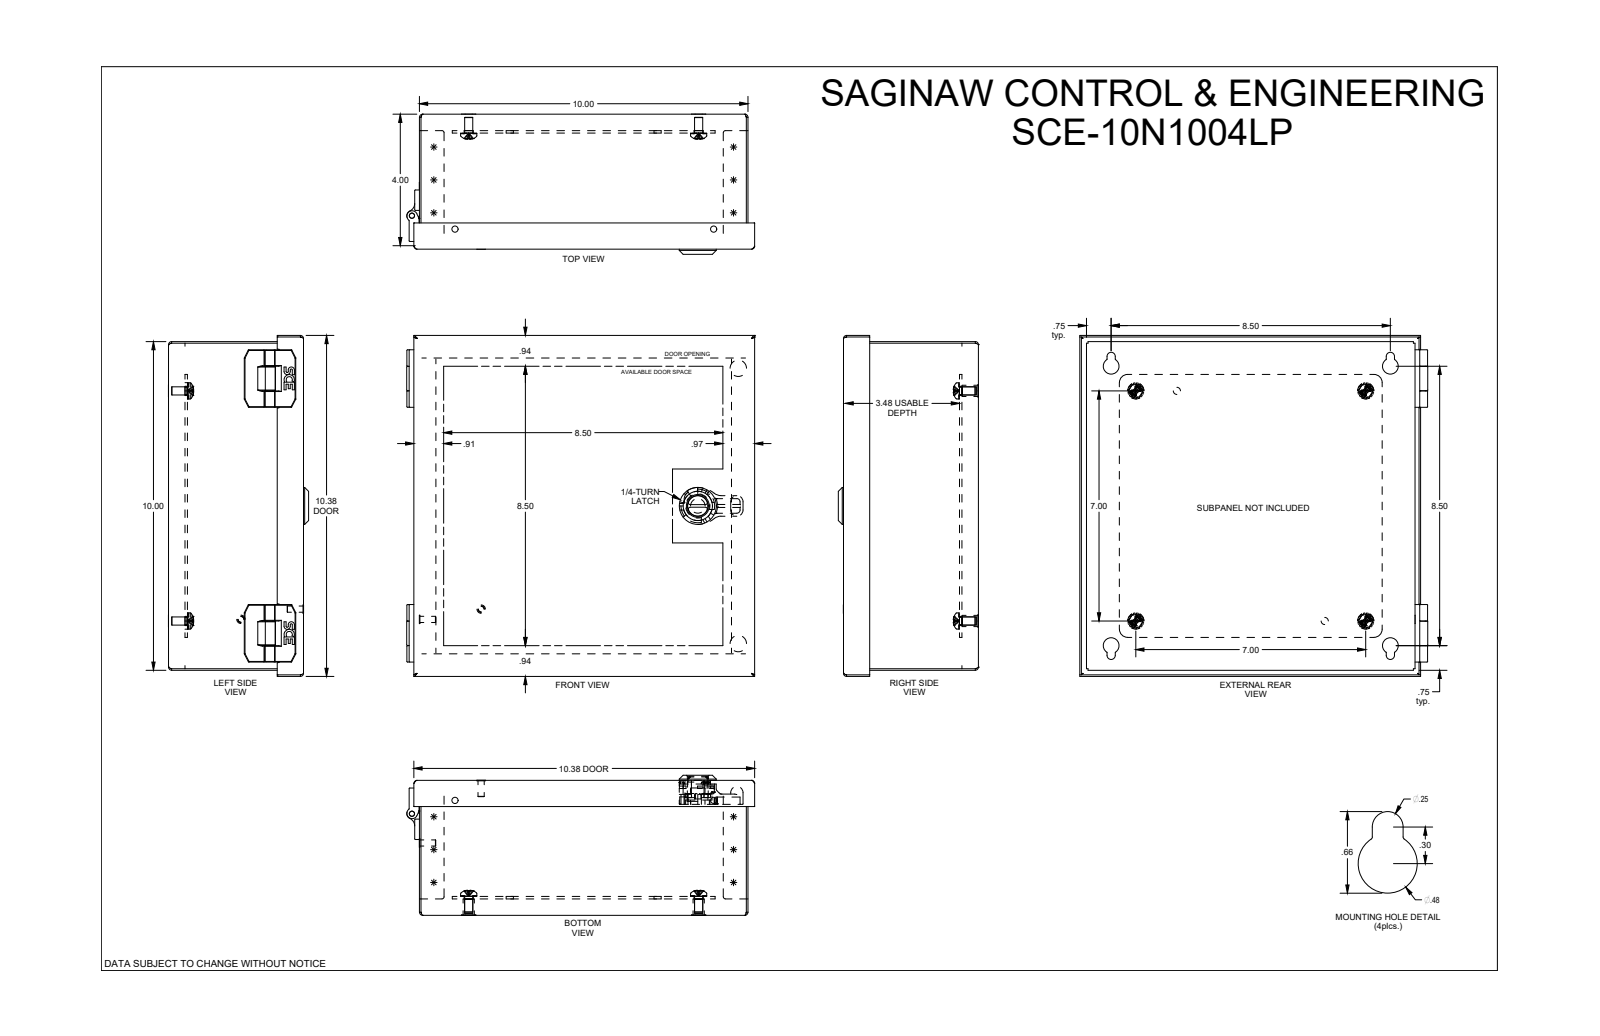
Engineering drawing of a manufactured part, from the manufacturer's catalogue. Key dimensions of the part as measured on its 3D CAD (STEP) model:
Part name (STEP PRODUCT): SCE-10N1004LP
STEP written by: SolidWorks 2019 (AUTOMOTIVE_DESIGN)
Units: inches
Bodies: 31 solids, 1546 faces (578 planar, 644 cylindrical, 324 other)
Overall size (bounding box): 10.592 × 10.375 × 4.267
Volume: 31.31 in³ · Surface area: 998.4 in²
Round holes (diameter × count): ⌀0.17 ×4, ⌀0.25 ×4, ⌀0.281 ×4, ⌀0.329 ×4, ⌀0.343 ×4, ⌀0.48 ×4, ⌀0.187 ×2, ⌀0.193 ×2, ⌀0.218 ×2, ⌀0.158 ×1, ⌀0.44 ×1, ⌀0.635 ×1
Round bosses / shafts (diameter × count): ⌀0.492 ×4, ⌀0.479 ×4, ⌀0.341 ×4, ⌀0.248 ×4, ⌀0.237 ×4, ⌀0.16 ×4, ⌀0.5 ×2, ⌀0.323 ×2
Partial cylindrical surfaces — rounded edges, fillets, slot ends (radius × count): R0.01 ×253, R0.02 ×95, R0.06 ×25, R0.015 ×24, R0.025 ×24, R0.055 ×6, R0.25 ×6, R0.125 ×4
Main face-to-face distances: 0.06, 4.048, 9.94, 3.989, 4.108, 10, 9.88, 0.5, 0.44, 0.575
Hole centre spacings: 7.786, 1.061, 7, 8.5, 10.96, 7.75, 7.75, 7.826
